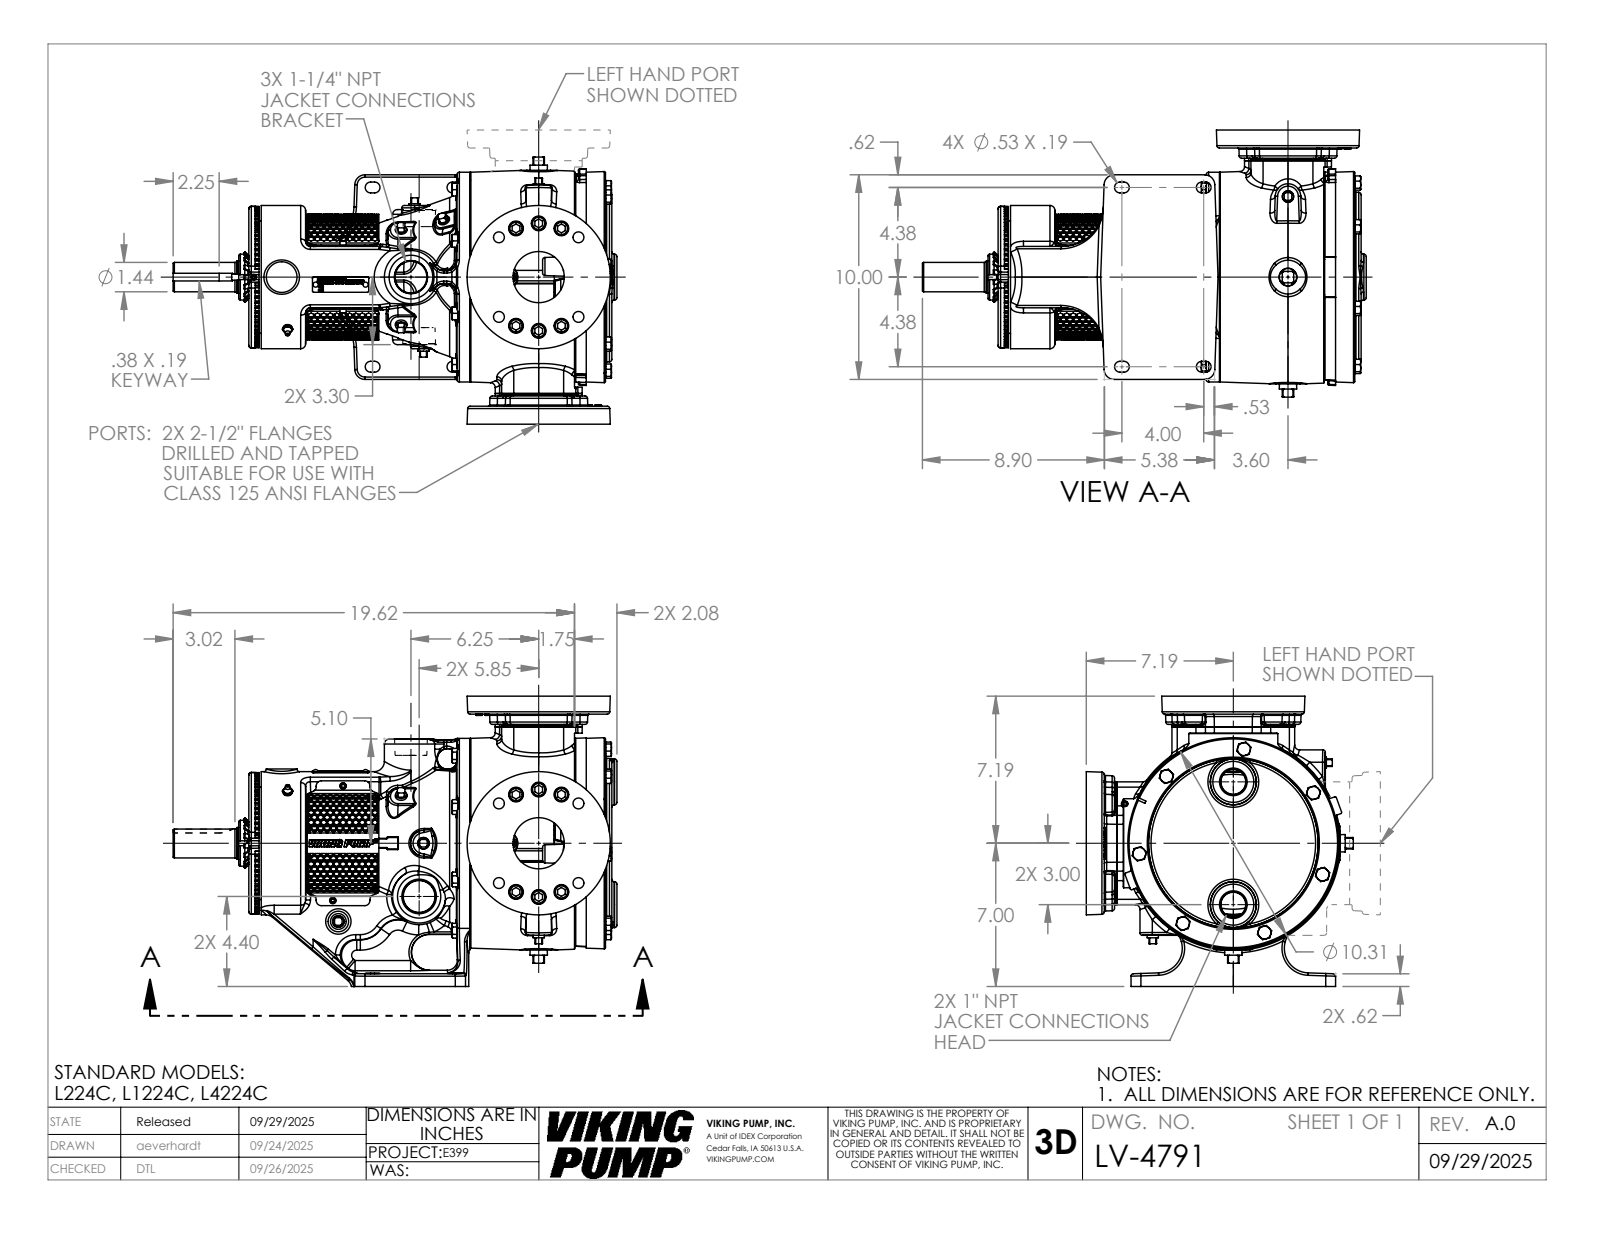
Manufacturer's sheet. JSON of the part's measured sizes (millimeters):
{"part_name": "LV-4791", "step_written_by": "SolidWorks 2024 (AUTOMOTIVE_DESIGN)", "units": "millimeters", "bodies": {"solids": 1, "faces": 5142, "planar": 1502, "cylindrical": 911, "other": 2729}, "overall_size": [551.1, 360.4, 331.5], "volume_mm3": 17980000, "surface_area_mm2": 876800, "round_holes": [[18.3, 12], [13.5, 8], [27.8, 8], [5.1, 6], [6.4, 6], [4, 3], [6.8, 2], [8, 2], [63.5, 2], [11.5, 1], [62, 1], [133.4, 1]], "round_bosses_or_shafts": [[16.8, 12], [15.9, 9], [15.9, 6], [11.1, 3], [7.9, 3], [260.4, 1], [177.8, 1], [139.6, 1]], "partial_cylinders_radius": [[1.6, 109], [1.8, 74], [3, 58], [0.3, 34], [0.2, 28], [12.7, 26], [0.8, 18], [1.5, 17]], "face_to_face_distances": [360.3, 7.9, 373, 380.9, 57.2, 12.7, 89.8, 283.2, 291.1, 69.9], "hole_center_spacings": [76.2, 69.9, 66.7, 34.9, 23.9, 28.9, 52.3, 55.4]}
